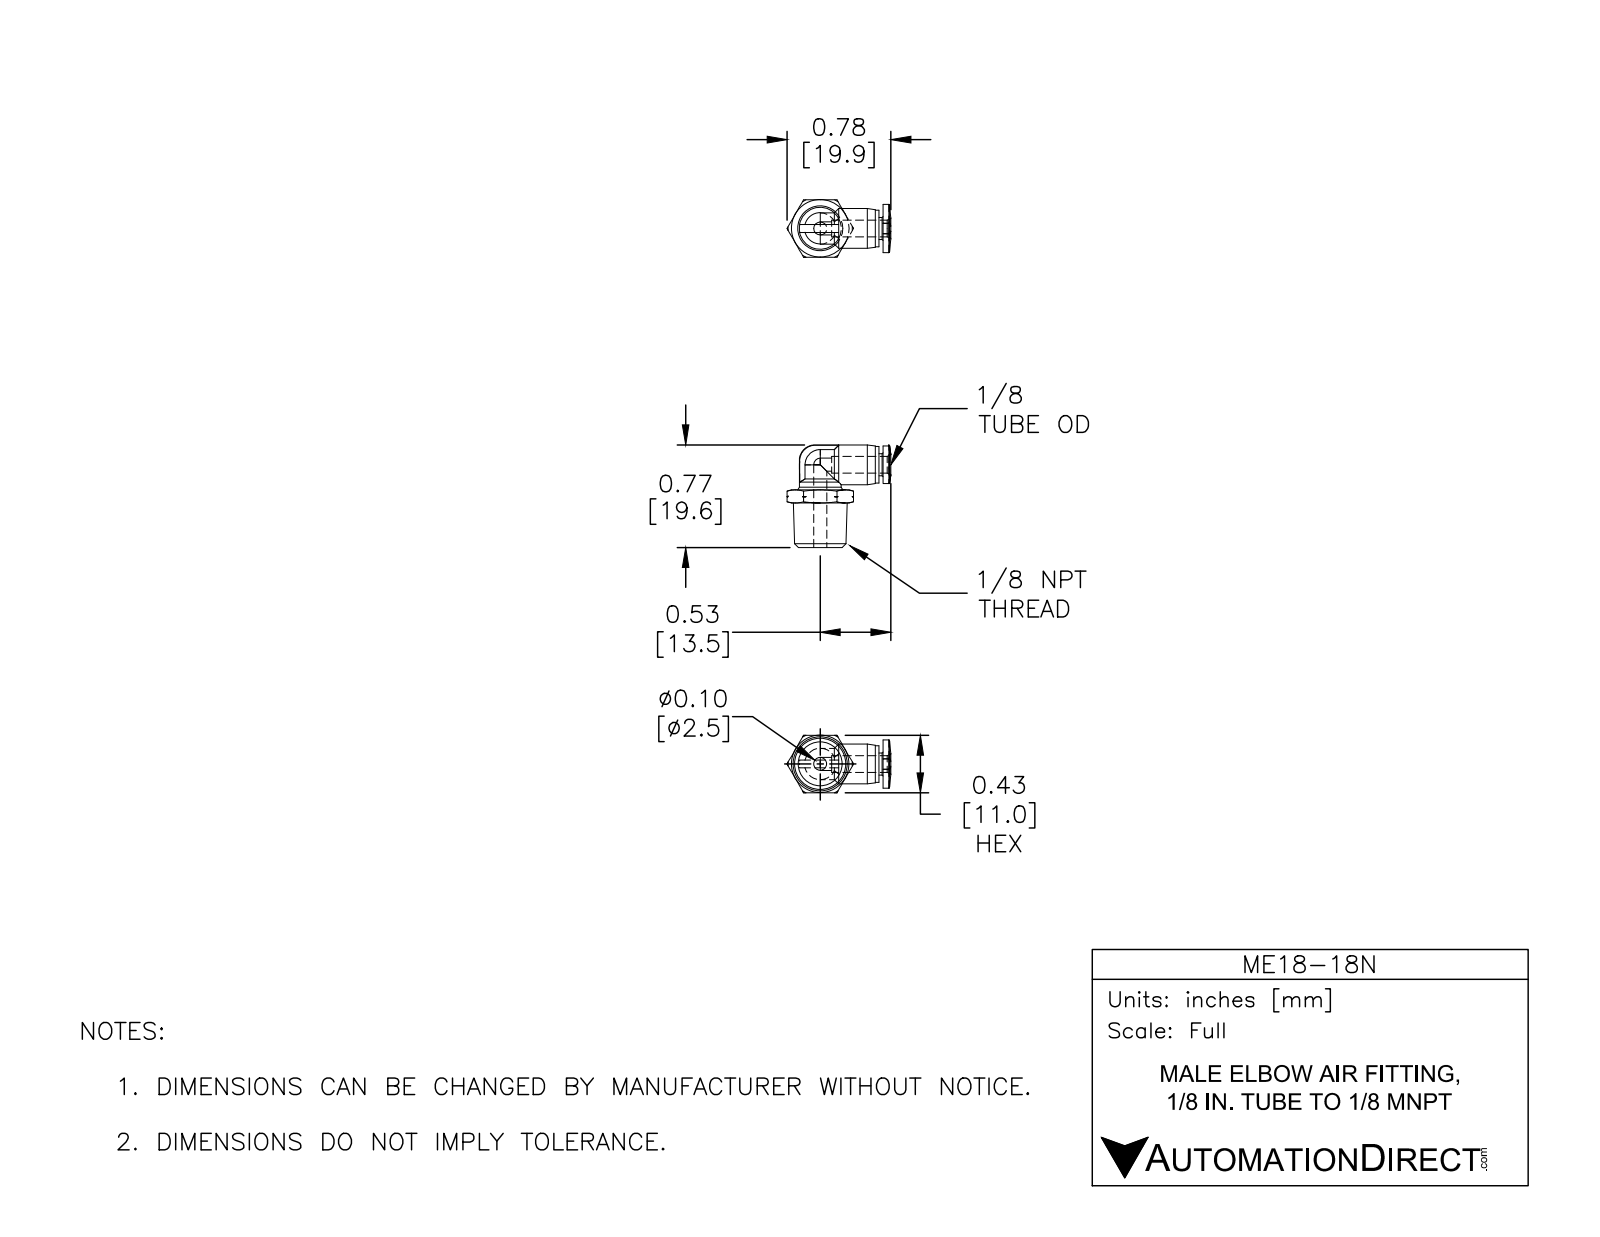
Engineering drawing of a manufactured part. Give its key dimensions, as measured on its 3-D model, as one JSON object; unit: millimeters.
{"part_name": "ME18-18N", "step_written_by": "SolidWorks 2015 (CONFIG_CONTROL_DESIGN)", "units": "millimeters", "bodies": {"solids": 1, "faces": 101, "planar": 18, "cylindrical": 20, "other": 63}, "overall_size": [19.9, 19.6, 11], "volume_mm3": 1500, "surface_area_mm2": 1277, "round_holes": [[2.5, 2], [3.2, 1]], "round_bosses_or_shafts": [[8, 1], [7.6, 1], [7, 1], [4.2, 1]], "partial_cylinders_radius": [[3, 2], [3.6, 2]], "face_to_face_distances": [11, 0.8, 4.7, 6.2, 1.5, 8.5, 2.5, 9, 9.8, 19.4]}
